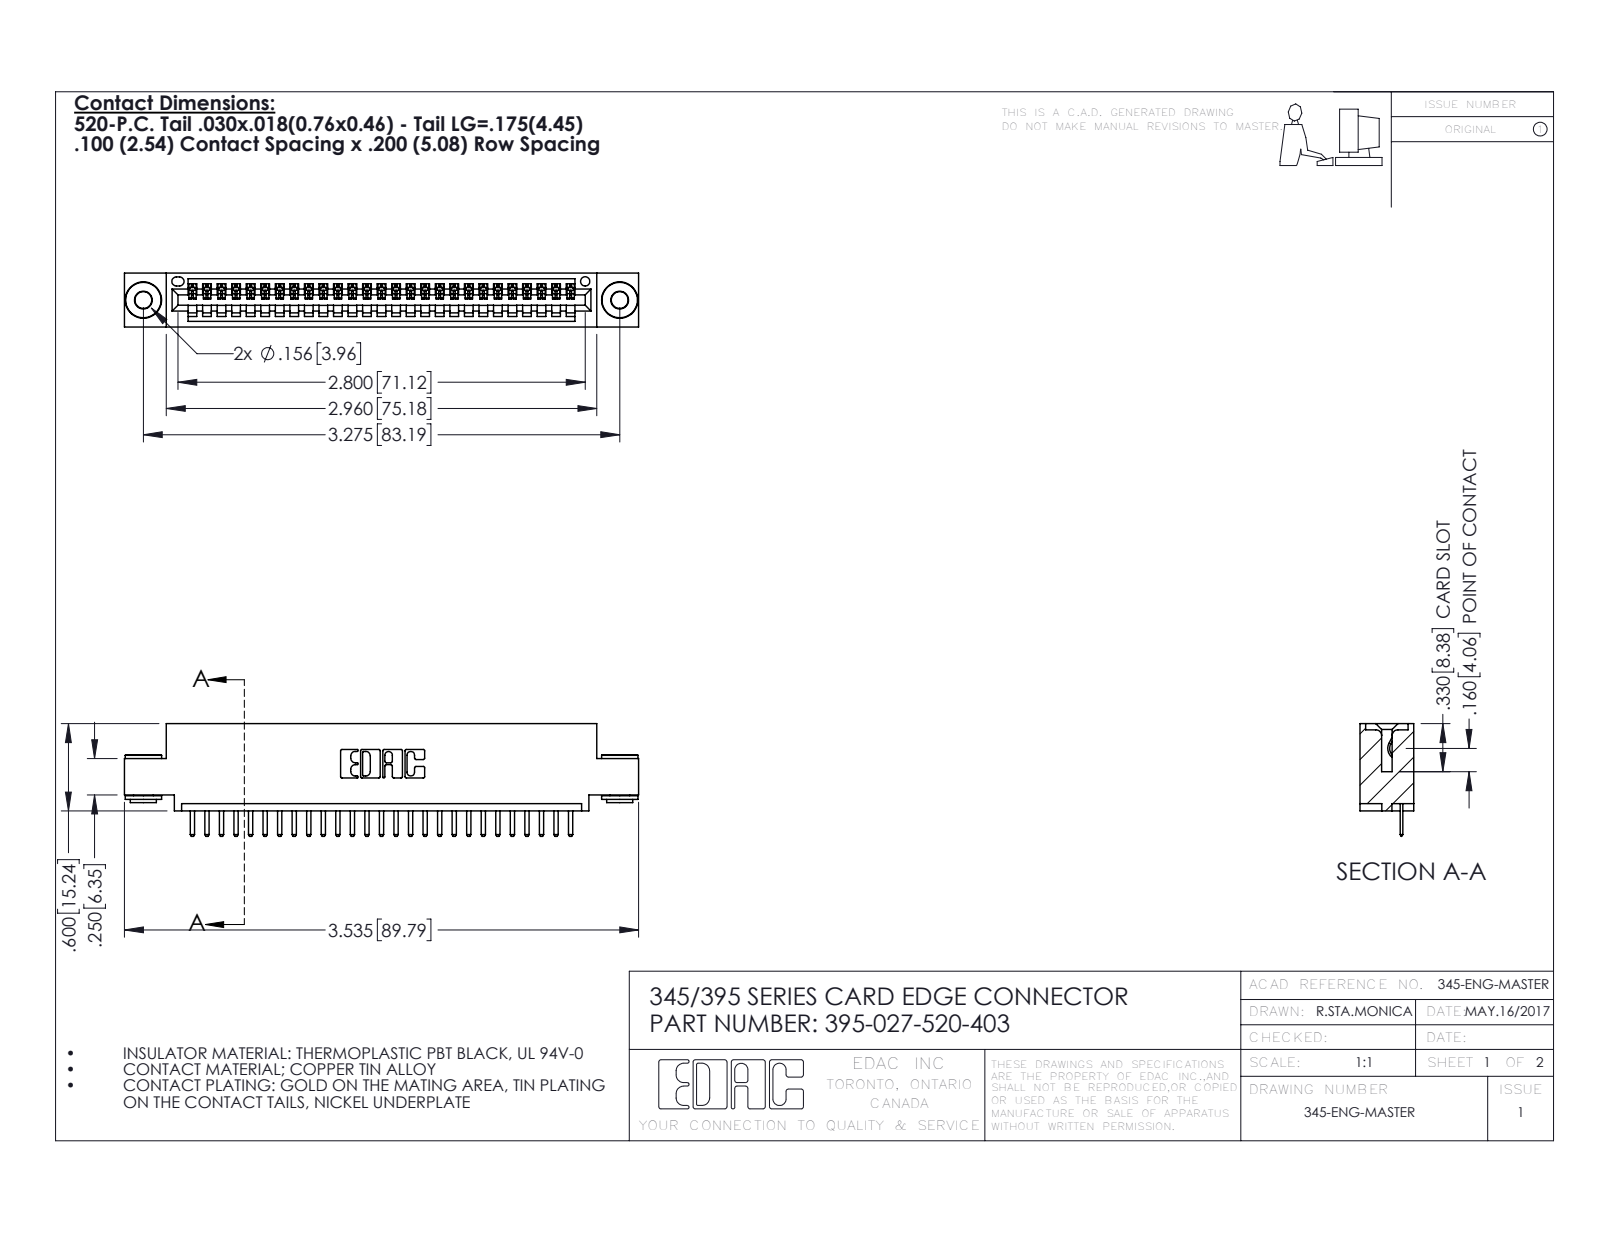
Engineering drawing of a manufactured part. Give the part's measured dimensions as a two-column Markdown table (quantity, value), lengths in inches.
| quantity | value |
| --- | --- |
| part name | 345-292-001_345-293-120; 345-250-002_345-250-002-102; 395-027-520-403; 345 Part_0.110 Offset - 0.156 Dia-TH |
| STEP written by | SolidWorks 2016 (CONFIG_CONTROL_DESIGN) |
| units | inches |
| bodies | 30 solids, 1842 faces (1228 planar, 606 cylindrical, 8 other) |
| overall size | 3.535 × 0.775 × 0.37 |
| volume | 0.505 in³ |
| surface area | 16.79 in² |
| round holes (diameter × count) | 0.116 × 2, 0.156 × 2, 0.064 × 1 |
| round bosses / shafts (diameter × count) | 0.25 × 2, 0.18 × 2, 0.136 × 2 |
| partial cylindrical surfaces (radius × count) | 0.01 × 56, 0.006 × 54, 0.01 × 22, 0.007 × 6, 0.031 × 6, 0.026 × 3, 0.031 × 2, 0.04 × 2 |
| main face-to-face distances | 0.072, 0.298, 0.37, 0.2, 0.025, 0.098, 0.272, 0.225, 0.072, 0.149 |
| hole center spacings | 0.27, 3.04, 3.275 |
